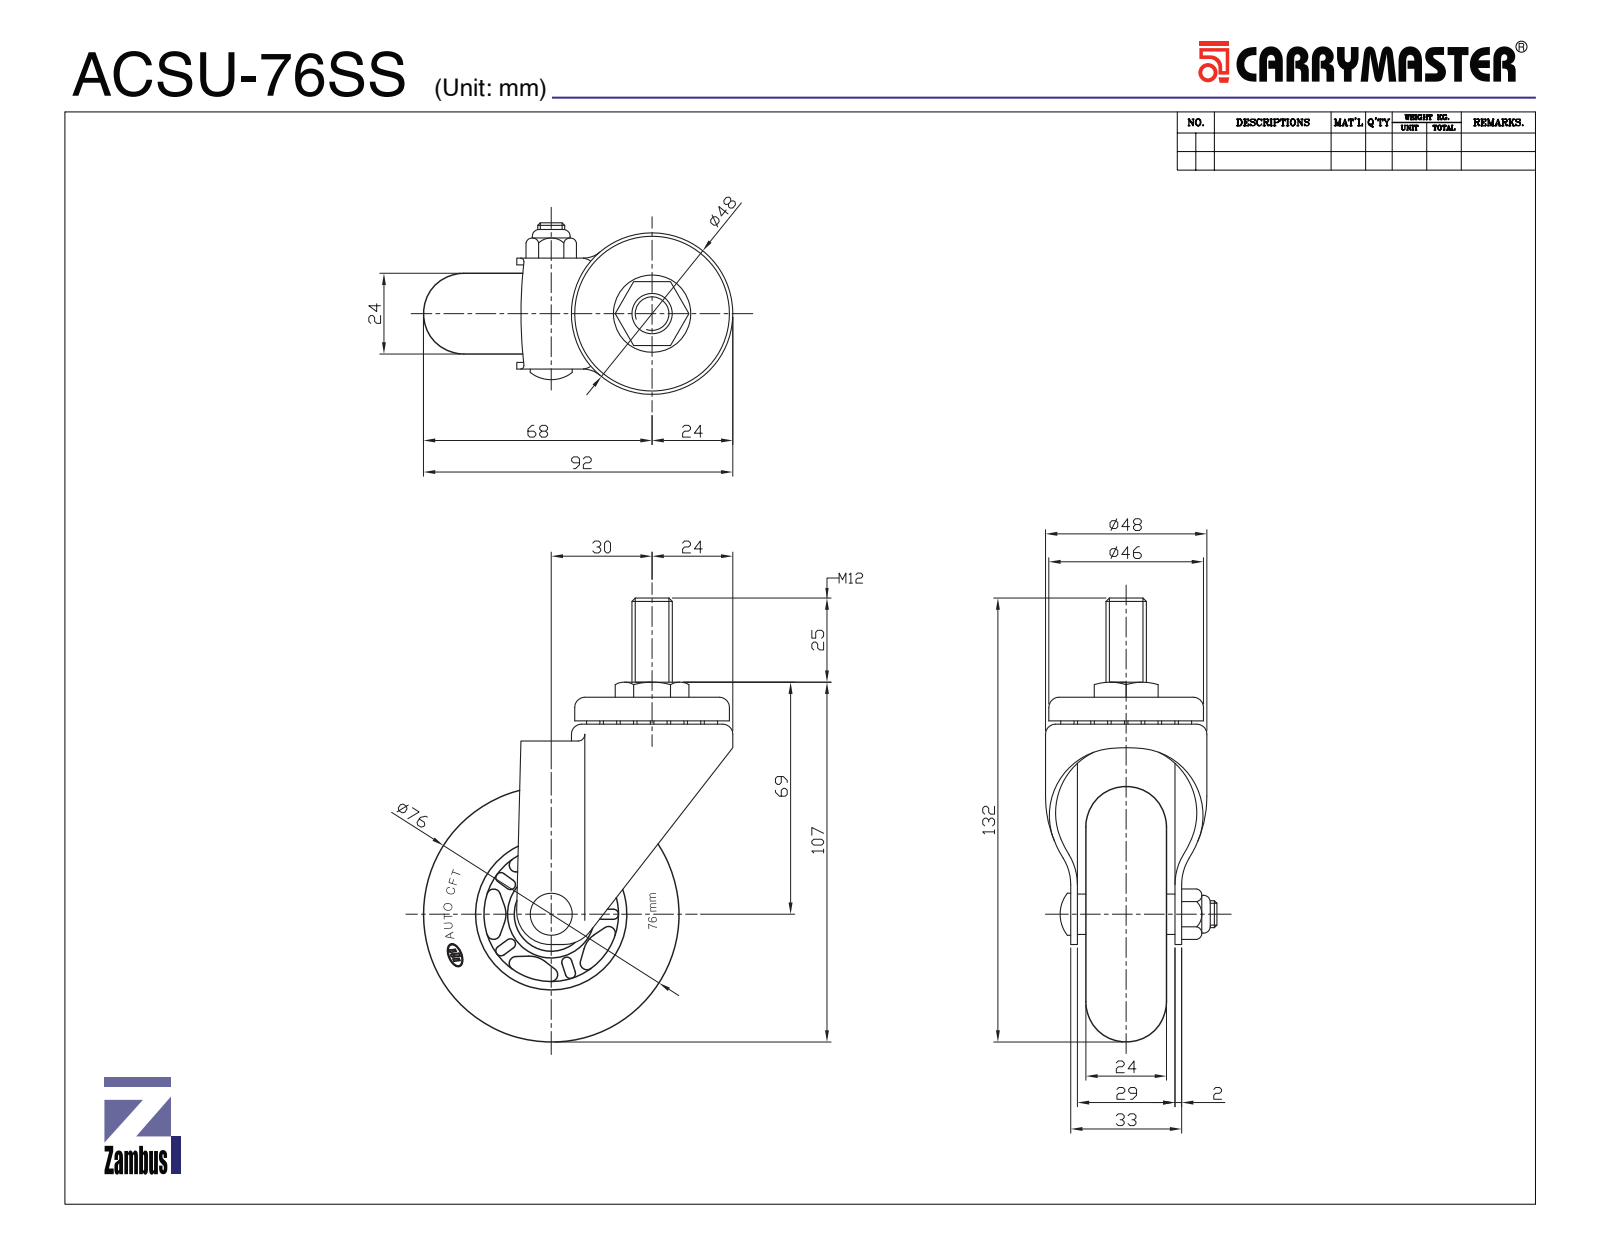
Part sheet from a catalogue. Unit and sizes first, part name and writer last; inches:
Units: inches
Overall size (bounding box): 5.26 × 3.652 × 1.927
Round holes (diameter × count): ⌀0.268 ×1, ⌀0.315 ×1, ⌀0.319 ×1, ⌀0.433 ×1, ⌀0.682 ×1, ⌀0.728 ×1, ⌀0.866 ×1, ⌀1.063 ×1, ⌀1.543 ×1, ⌀1.713 ×1, ⌀1.732 ×1
Round bosses / shafts (diameter × count): ⌀1.87 ×1, ⌀1.669 ×1, ⌀1.193 ×1, ⌀0.709 ×1, ⌀0.63 ×1, ⌀0.499 ×1, ⌀0.492 ×1, ⌀0.472 ×1
Partial cylindrical surfaces — rounded edges, fillets, slot ends (radius × count): R0.039 ×48, R0.059 ×25, R0.118 ×7, R0.394 ×3, R0.02 ×2, R0.315 ×2, R0.315 ×1, R0.787 ×1
Main face-to-face distances: 0.079, 1.378, 0.256, 0.177, 0.276, 1.201, 1.122, 0.138, 0.252, 1.457
Volume: 7.404 in³ · Surface area: 103.4 in²
Bodies: 13 solids, 545 faces (142 planar, 246 cylindrical, 157 other)
Part name (STEP PRODUCT): ACSU-76SS
STEP written by: SolidWorks 2015 (CONFIG_CONTROL_DESIGN)
